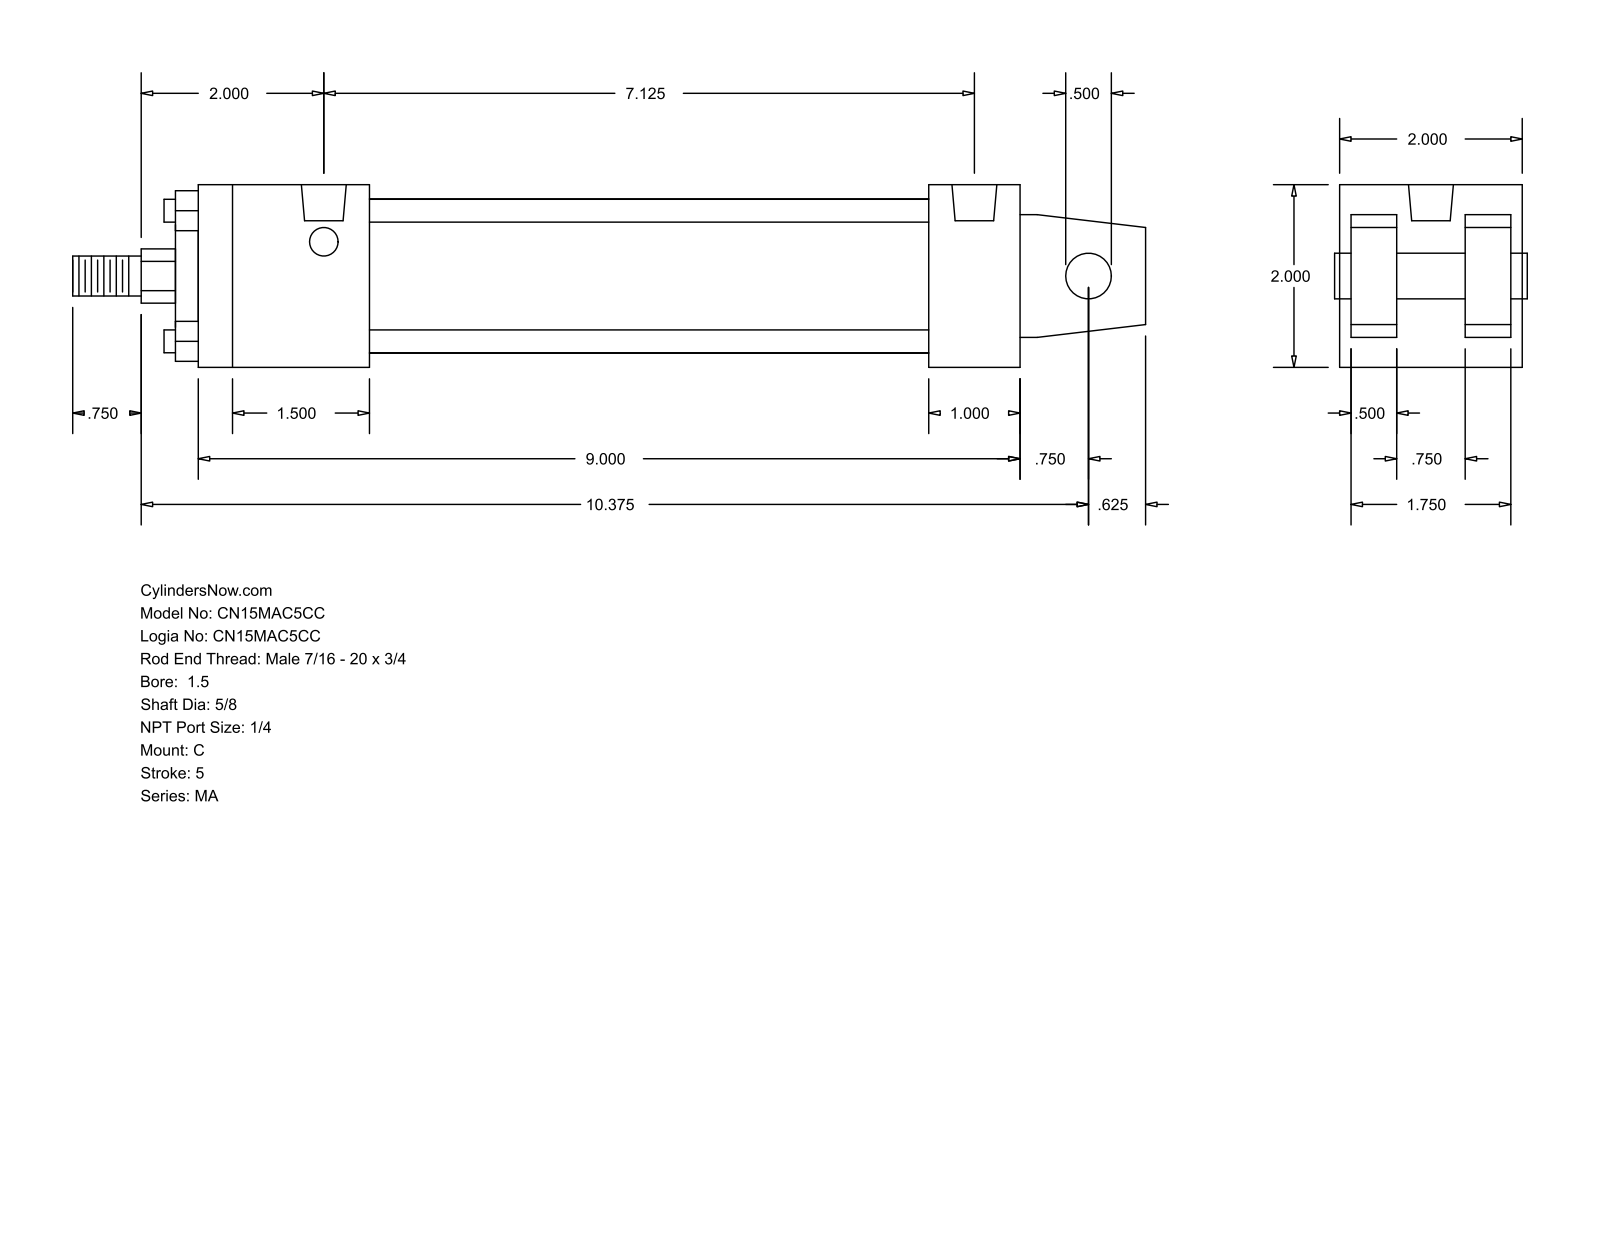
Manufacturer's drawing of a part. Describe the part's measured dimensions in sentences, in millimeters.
The part is named "MA_C__0150_0.625". Its 3-D file was written by "GSSL Pune (CONFIG_CONTROL_DESIGN)". It is 0 solids with 103 faces: 76 planar, 27 cylindrical and 0 other. Overall it measures 298.45 by 50.8 by 50.8 millimeters. Round holes: 4 of diameter 7.94, 2 of diameter 12.49. Round bosses or shafts: 4 of diameter 6.35, 1 of diameter 42.93, 1 of diameter 28.57, 1 of diameter 15.88, 1 of diameter 12.7, 1 of diameter 11.11. Partial cylindrical surfaces (rounded edges, fillets, slot ends): 1 of radius 7.54. The main face-to-face distances are 50.8, 34.93, 12.7, 15.87, 3.17, 47.63, 31.76, 228.59, 25.4, 203.19. The hole center spacings are 180.98.
